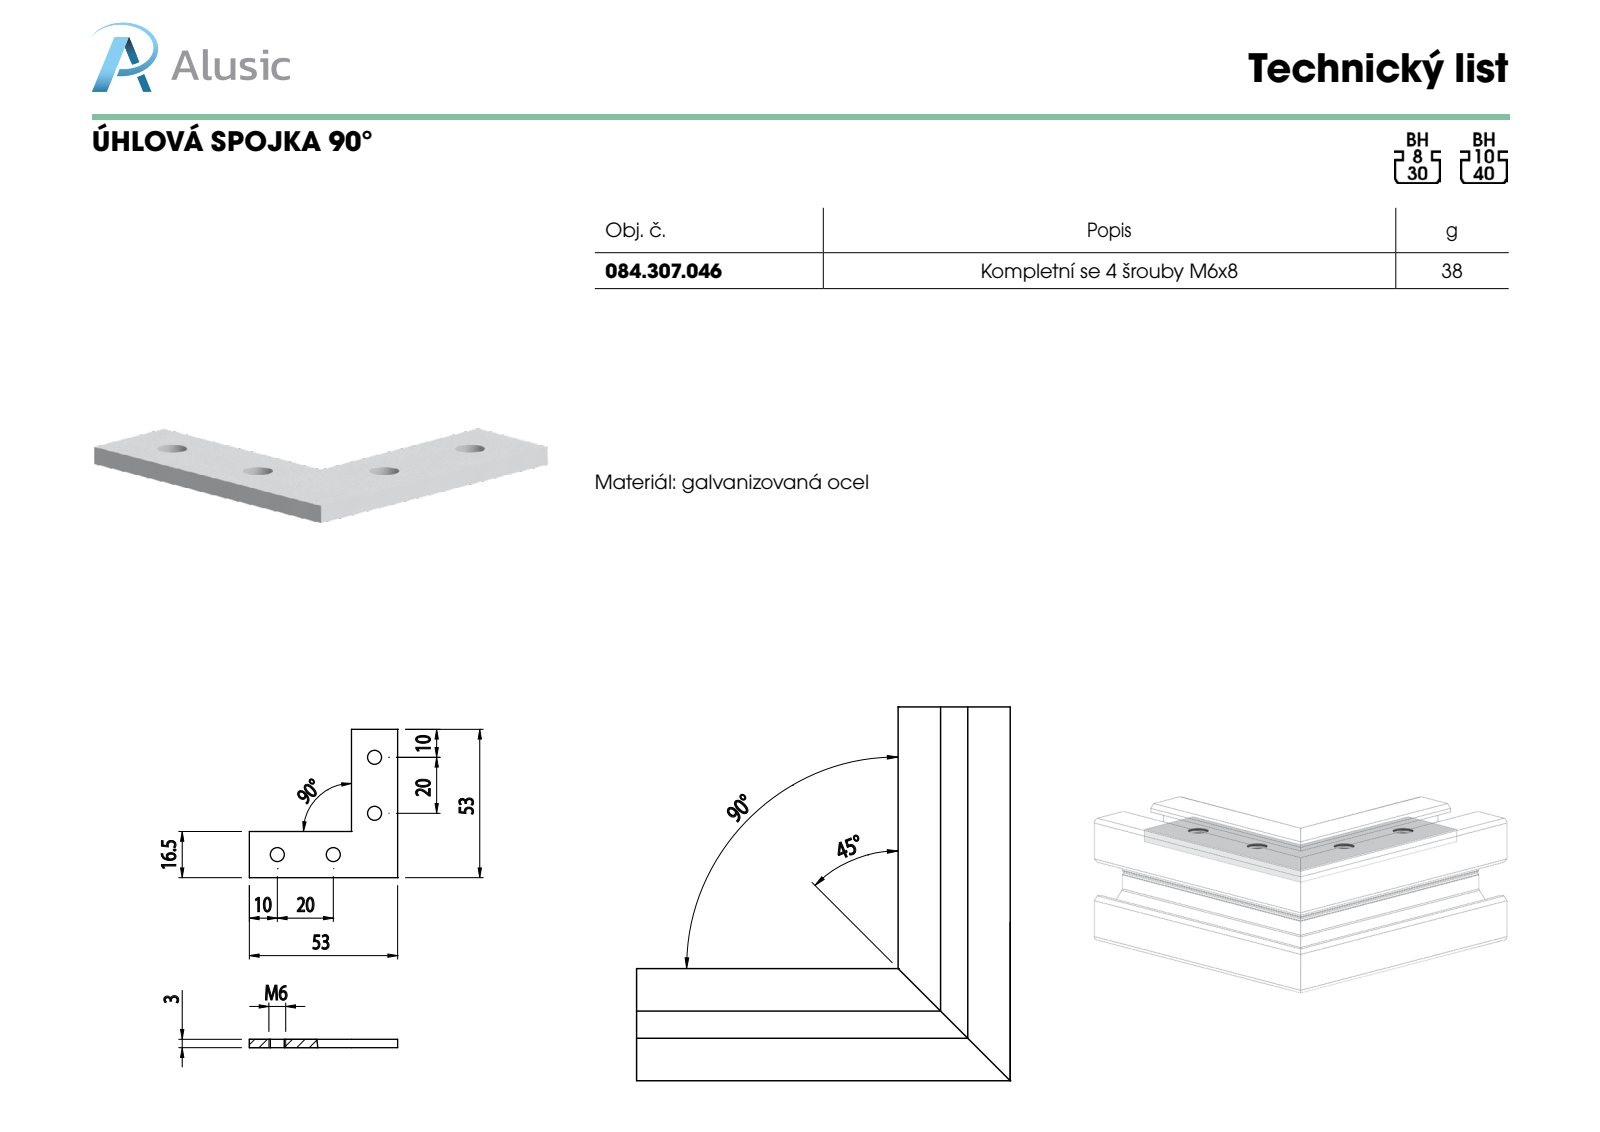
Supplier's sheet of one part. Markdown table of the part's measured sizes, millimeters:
| quantity | value |
| --- | --- |
| part name | 084.307.046 |
| STEP written by | SolidWorks 2012 (CONFIG_CONTROL_DESIGN) |
| units | millimeters |
| bodies | 1 solid, 16 faces (8 planar, 8 cylindrical, 0 other) |
| overall size | 53 × 53 × 3 |
| volume | 4 195 mm³ |
| surface area | 3 621 mm² |
| round holes (diameter × count) | 5 × 4 |
| main face-to-face distances | 3, 16.5, 36.5, 53 |
| hole center spacings | 20, 37.75, 20.86, 49.14 |
